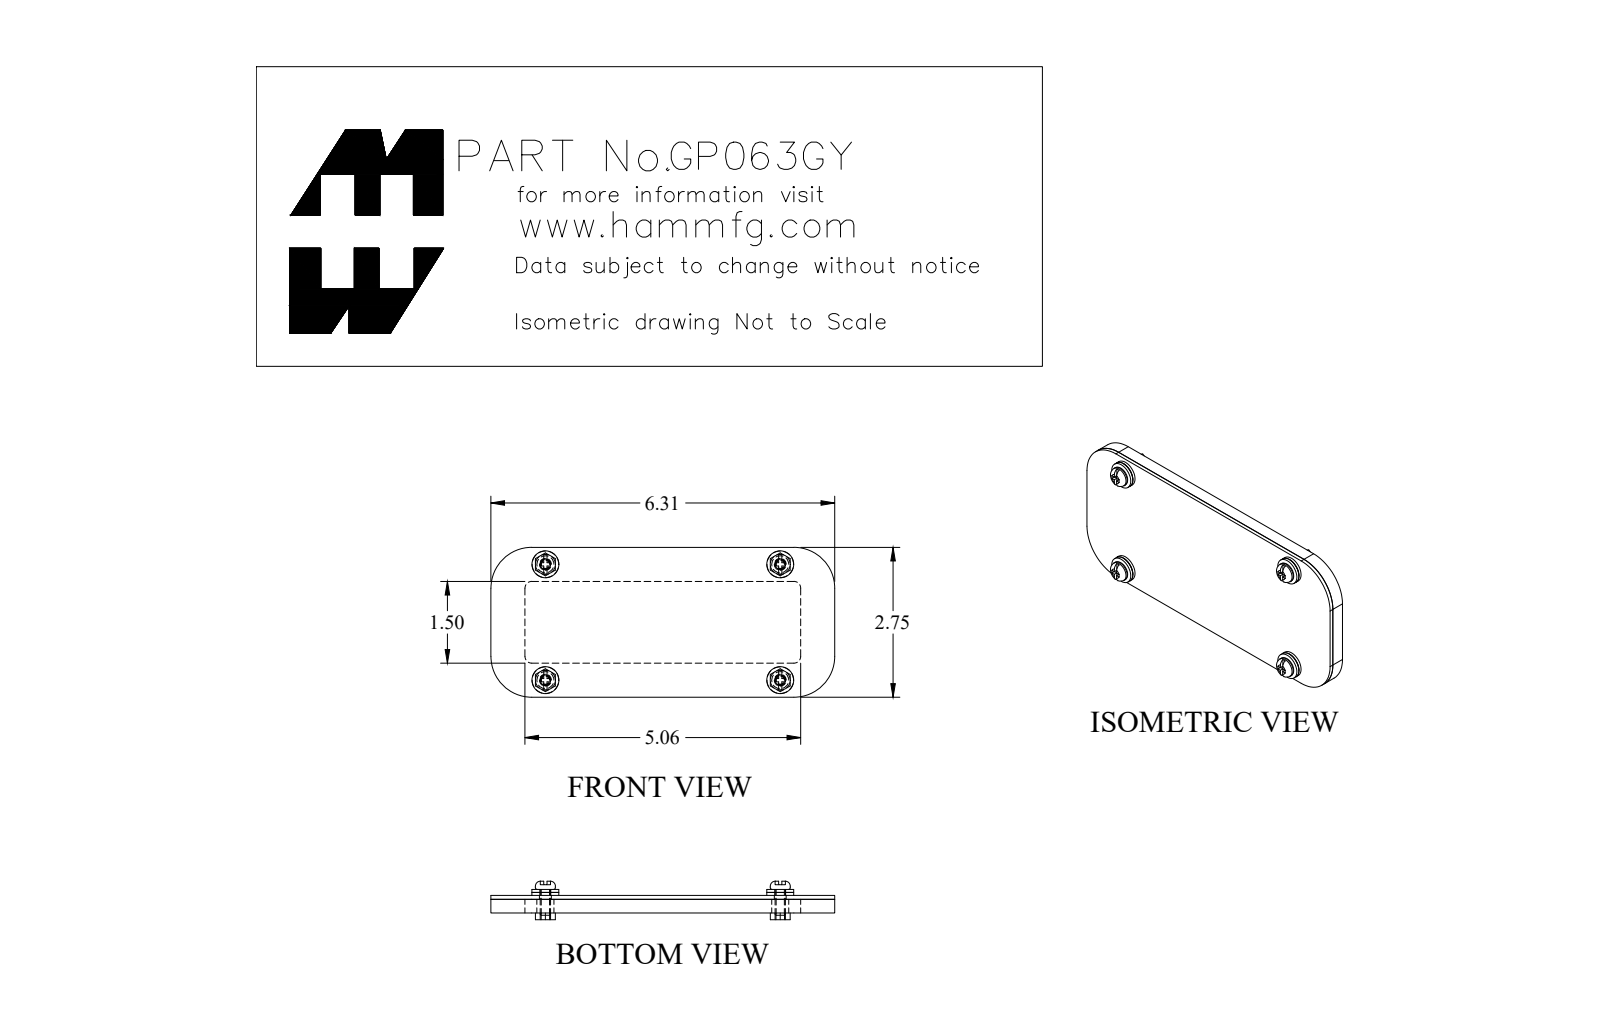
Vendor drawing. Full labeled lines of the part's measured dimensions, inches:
Part name (STEP PRODUCT): GP063GY
STEP written by: SolidWorks 2018 (AUTOMOTIVE_DESIGN)
Units: inches
Bodies: 14 solids, 240 faces (132 planar, 84 cylindrical, 24 other)
Overall size (bounding box): 6.312 × 2.75 × 0.707
Volume: 3.672 in³ · Surface area: 67.79 in²
Round holes (diameter × count): ⌀0.156 ×4, ⌀0.197 ×4, ⌀0.218 ×4, ⌀0.313 ×4
Round bosses / shafts (diameter × count): ⌀0.494 ×4, ⌀0.488 ×4, ⌀0.367 ×4, ⌀0.19 ×4
Partial cylindrical surfaces — rounded edges, fillets, slot ends (radius × count): R0.75 ×8, R0.125 ×4
Main face-to-face distances: 0.072, 0.322, 0.25, 0.625, 2.125, 2.125, 0.625, 2.75, 1.5, 0.11
Hole centre spacings: 2.125, 4.312, 4.807
